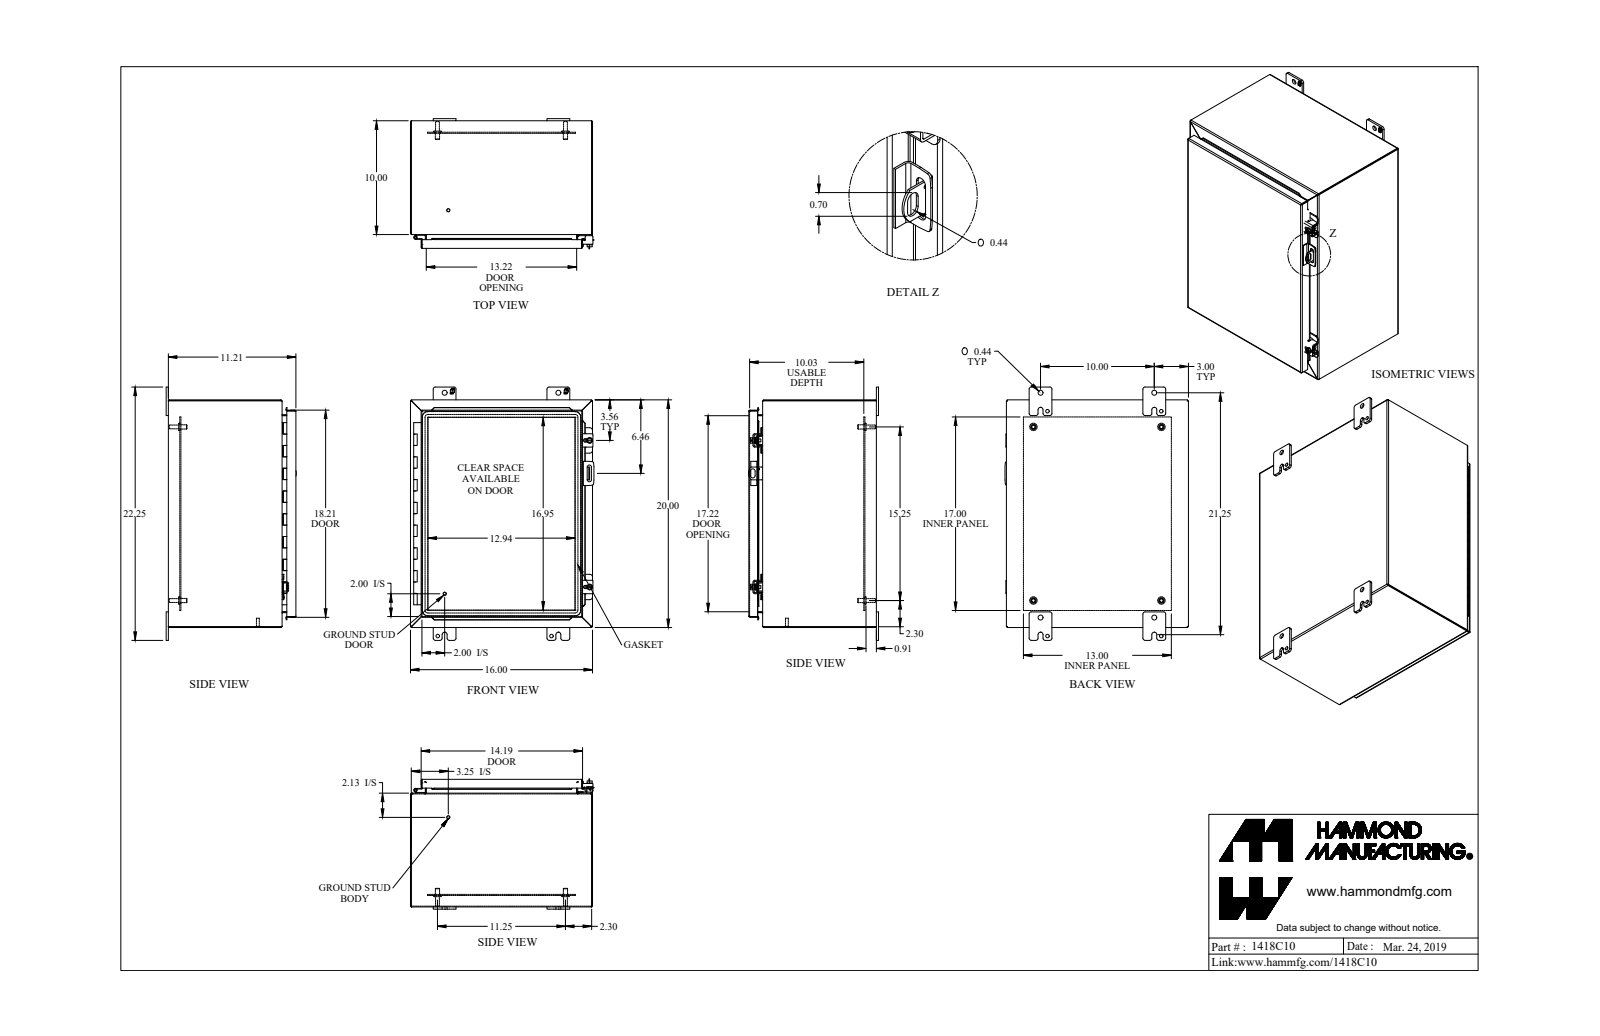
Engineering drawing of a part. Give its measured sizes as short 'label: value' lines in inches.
name: 1418C10
written by: SolidWorks 2019 (AUTOMOTIVE_DESIGN)
unit: in
bodies: 38 solids, 970 faces (667 planar, 251 cylindrical, 52 other)
size: 22.25 × 16.125 × 11.437
volume: 146.1 in³; area: 3 824 in²
holes: 4× ⌀0.313, 4× ⌀0.437, 4× ⌀0.5, 2× ⌀0.213, 2× ⌀0.265, 2× ⌀0.307, 2× ⌀0.375, 2× ⌀0.445, 1× ⌀0.125, 1× ⌀0.187
bosses: 4× ⌀0.65, 4× ⌀0.375, 4× ⌀0.33, 2× ⌀1, 2× ⌀0.5, 2× ⌀0.39, 2× ⌀0.281, 2× ⌀0.25
rounds: 26× R0.188, 20× R0.036, 20× R0.108, 13× R0.048, 13× R0.143, 8× R0.007, 8× R0.045, 8× R0.079
face distances: 0.072, 11.113, 15.928, 11.041, 19.928, 0.937, 11.185, 1.009, 0.095, 10.081
hole spacings: 10, 18.951, 1.736, 3.065, 10.73, 11.25, 16.762, 19.75
